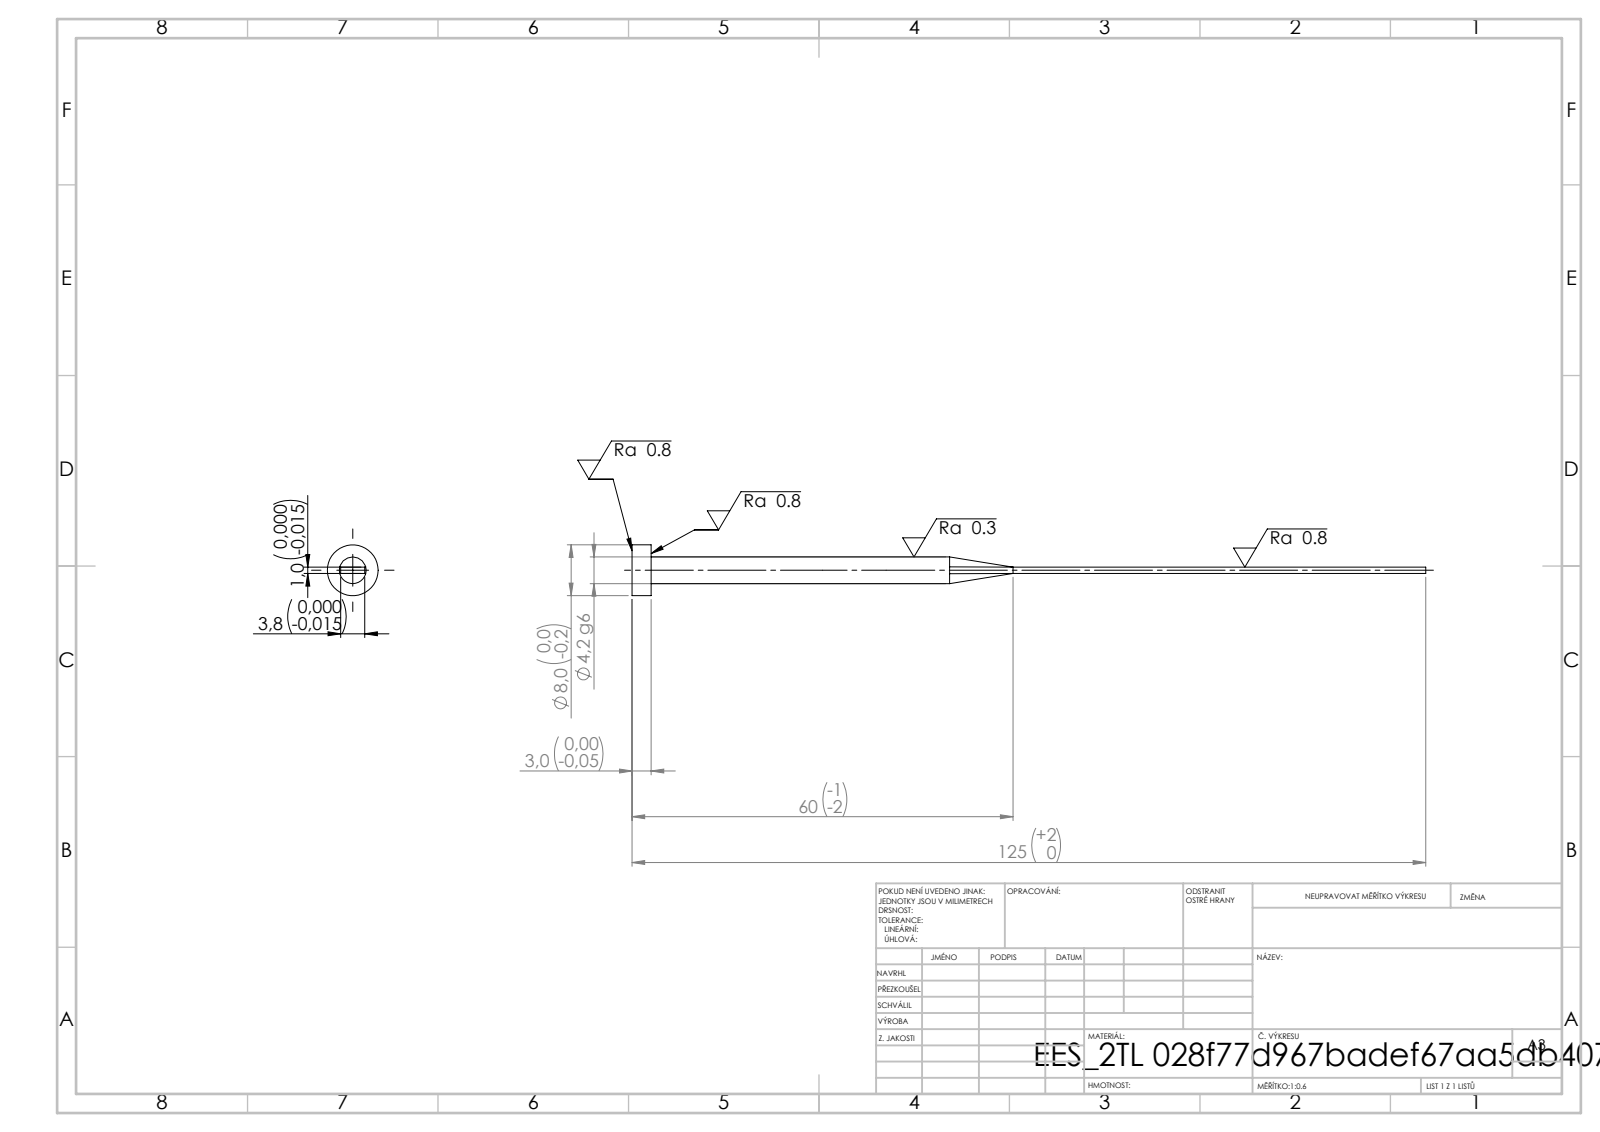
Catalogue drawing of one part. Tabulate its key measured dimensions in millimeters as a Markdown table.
| quantity | value |
| --- | --- |
| STEP written by | SolidWorks 2019 (CONFIG_CONTROL_DESIGN) |
| units | millimeters |
| bodies | 1 solid, 15 faces (7 planar, 4 cylindrical, 4 other) |
| overall size | 125 × 8 × 8 |
| volume | 1 133 mm³ |
| surface area | 1 520 mm² |
| round bosses / shafts (diameter × count) | 8 × 1, 4.2 × 1 |
| main face-to-face distances | 1, 3.8, 3, 125, 122 |
